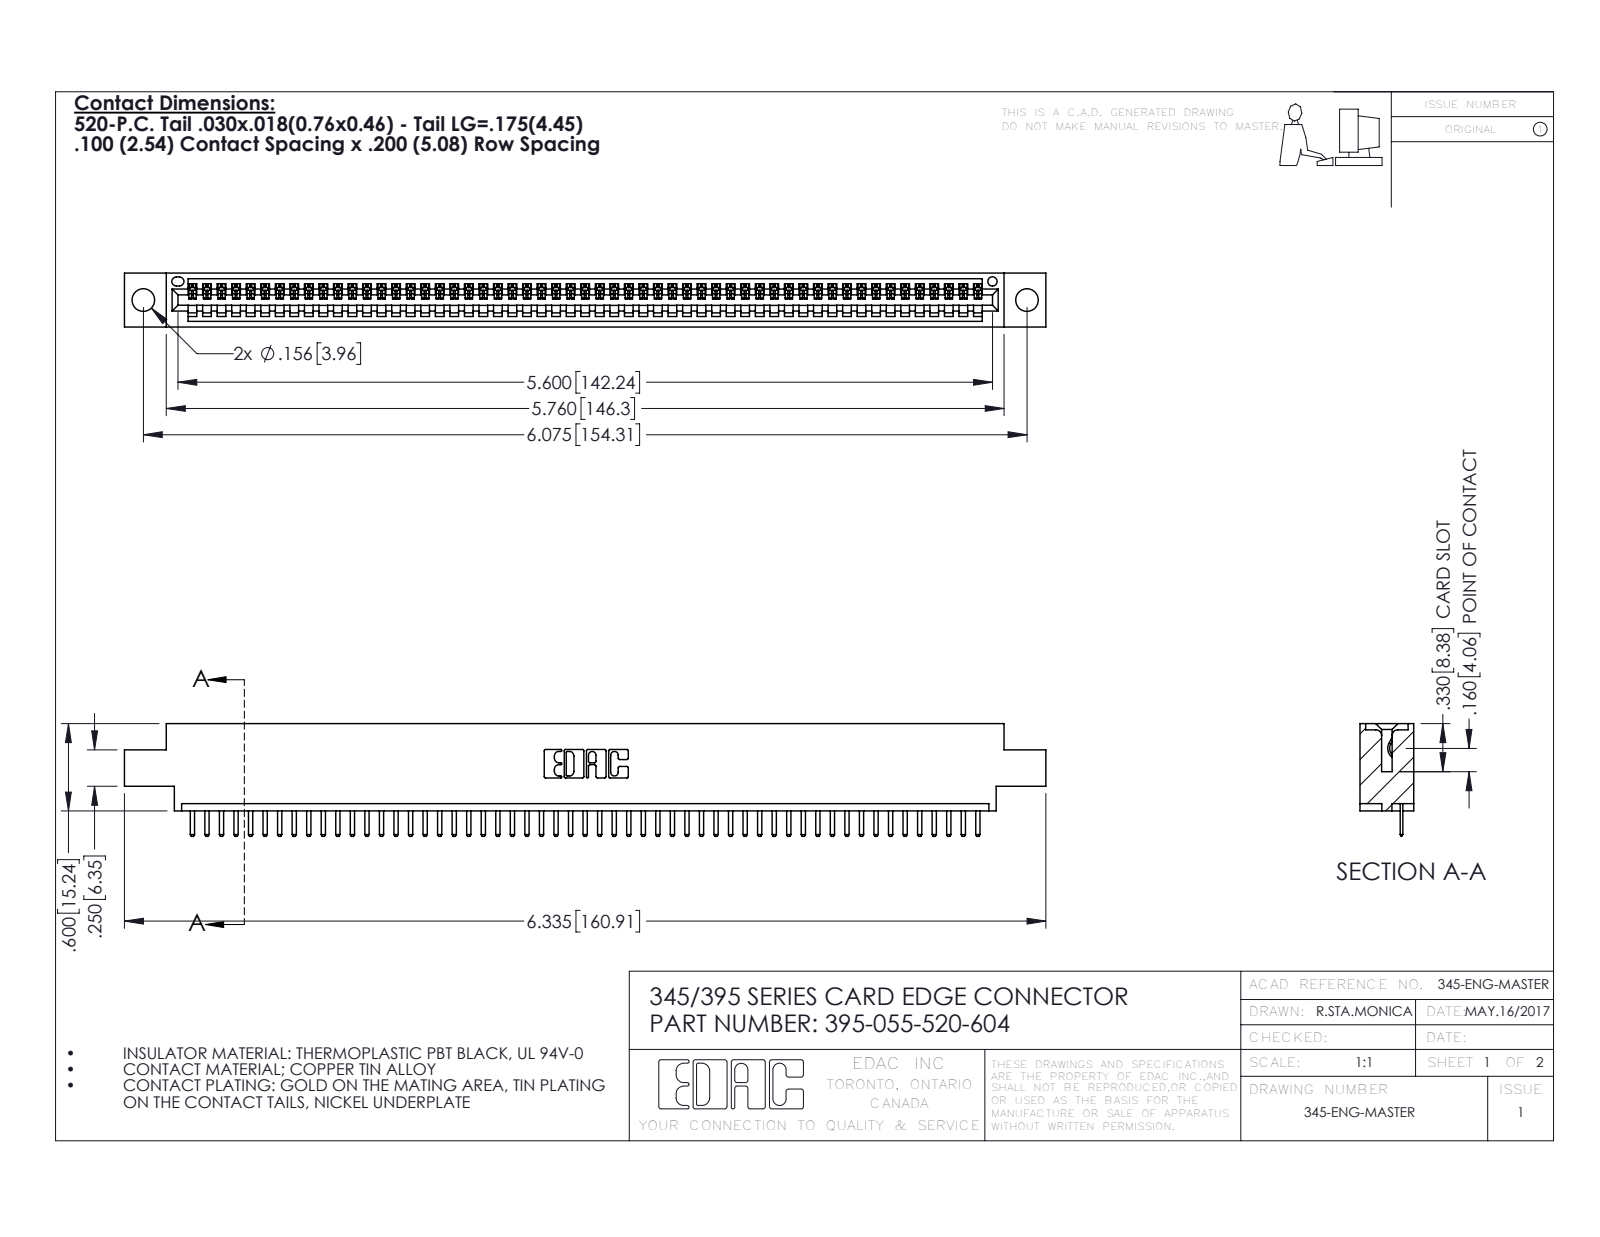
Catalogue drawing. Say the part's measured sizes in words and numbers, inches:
The part is named "345 Part_0.170 Offset - 0.156 Dia-TH; 345-292-001_345-293-120; 395-055-520-604". Its 3-D file was written by "SolidWorks 2016 (CONFIG_CONTROL_DESIGN)". It is 56 solids with 3540 faces: 2394 planar, 1146 cylindrical and 0 other. Overall it measures 6.335 by 0.775 by 0.37 inches. Its volume is 0.917 cubic inches and its surface area 30.33 square inches. Round holes: 2 of diameter 0.156, 1 of diameter 0.064. Partial cylindrical surfaces (rounded edges, fillets, slot ends): 112 of radius 0.01, 110 of radius 0.006, 22 of radius 0.01, 6 of radius 0.007, 6 of radius 0.031, 3 of radius 0.026, 2 of radius 0.031, 2 of radius 0.04. The main face-to-face distances are 0.298, 0.072, 0.37, 0.2, 0.098, 0.272, 0.025, 0.225, 0.072, 0.175. The hole center spacings are 0.27, 5.839, 6.075.
